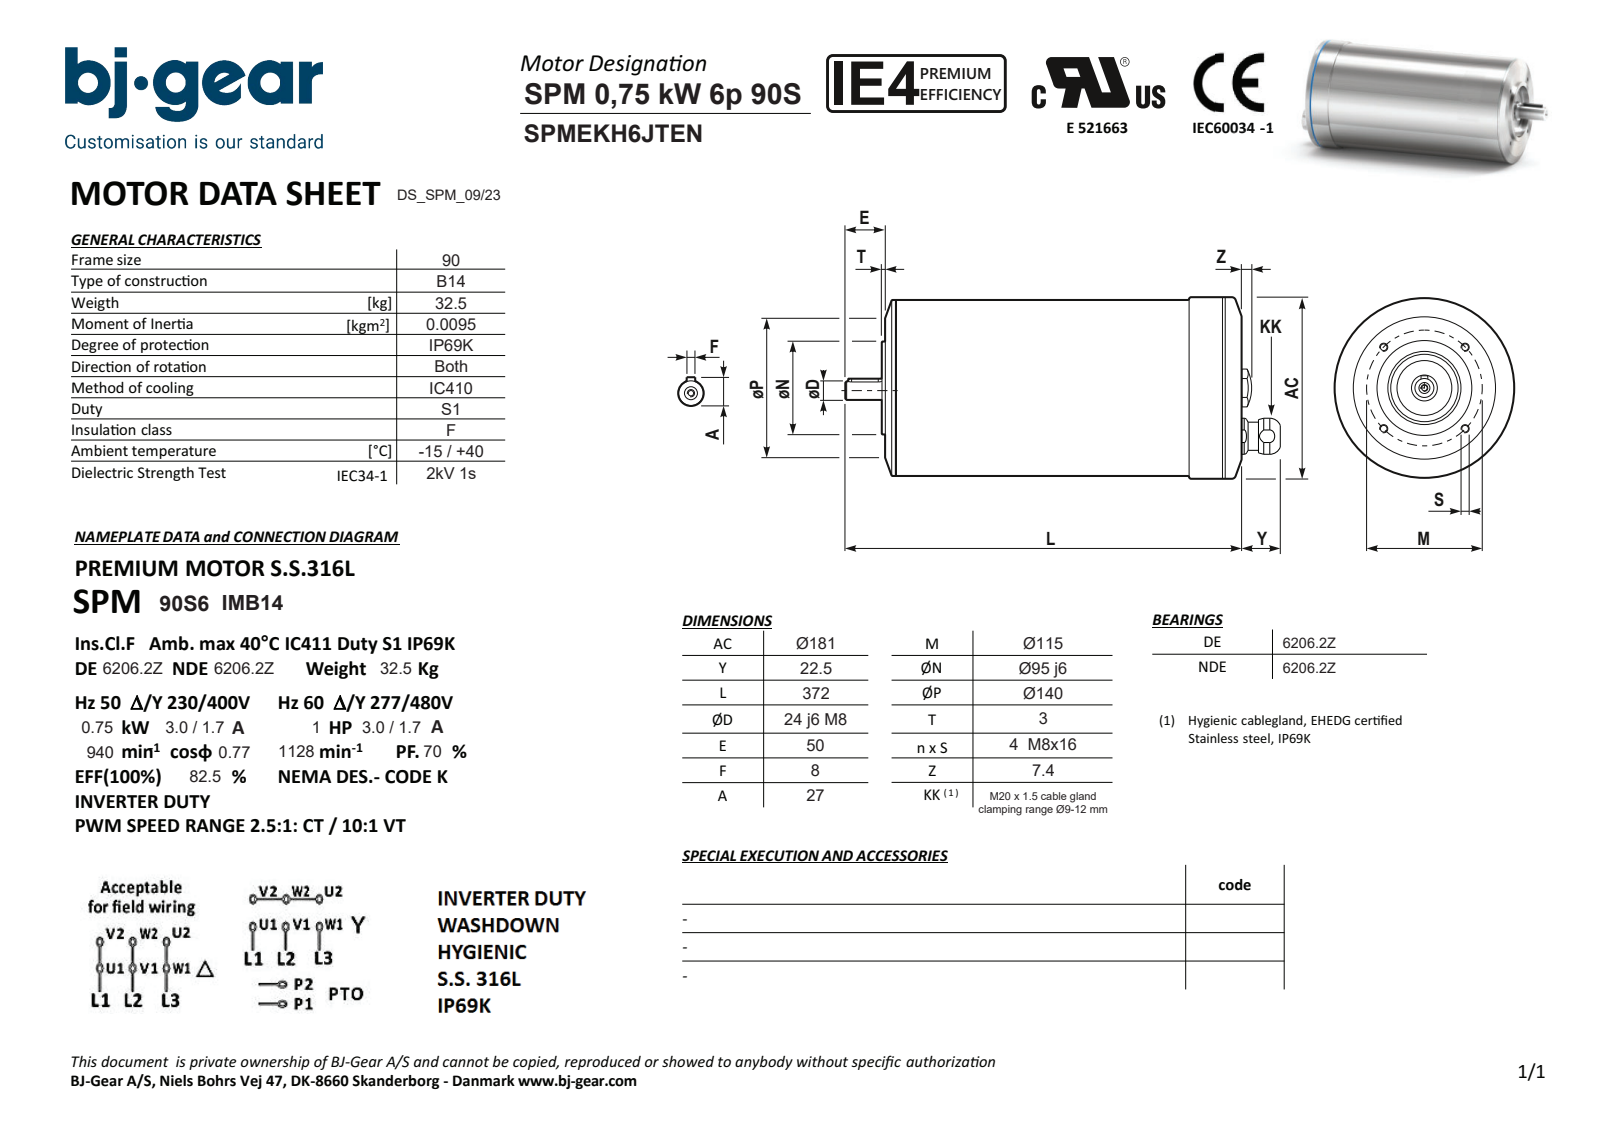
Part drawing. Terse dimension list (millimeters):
name: SPMEKH6JTENN4KSA1-N---NNN
written by: Solid Edge (AUTOMOTIVE_DESIGN)
unit: mm
bodies: 1 solid, 87 faces (30 planar, 32 cylindrical, 25 other)
size: 399.5 × 181 × 181
volume: 8 014 000 mm³; area: 238 617 mm²
holes: 4× ⌀6.65, 1× ⌀4.92, 1× ⌀7, 1× ⌀8.4, 1× ⌀13.4, 1× ⌀85
bosses: 1× ⌀181, 1× ⌀180.98, 1× ⌀178, 1× ⌀177.98, 1× ⌀95, 1× ⌀30, 1× ⌀24, 1× ⌀20
rounds: 2× R4, 1× R12.8
face distances: 322, 6, 316, 325, 9, 3, 8, 24, 50, 372
hole spacings: 57.5, 81.32, 43.11, 103.94, 115, 55
